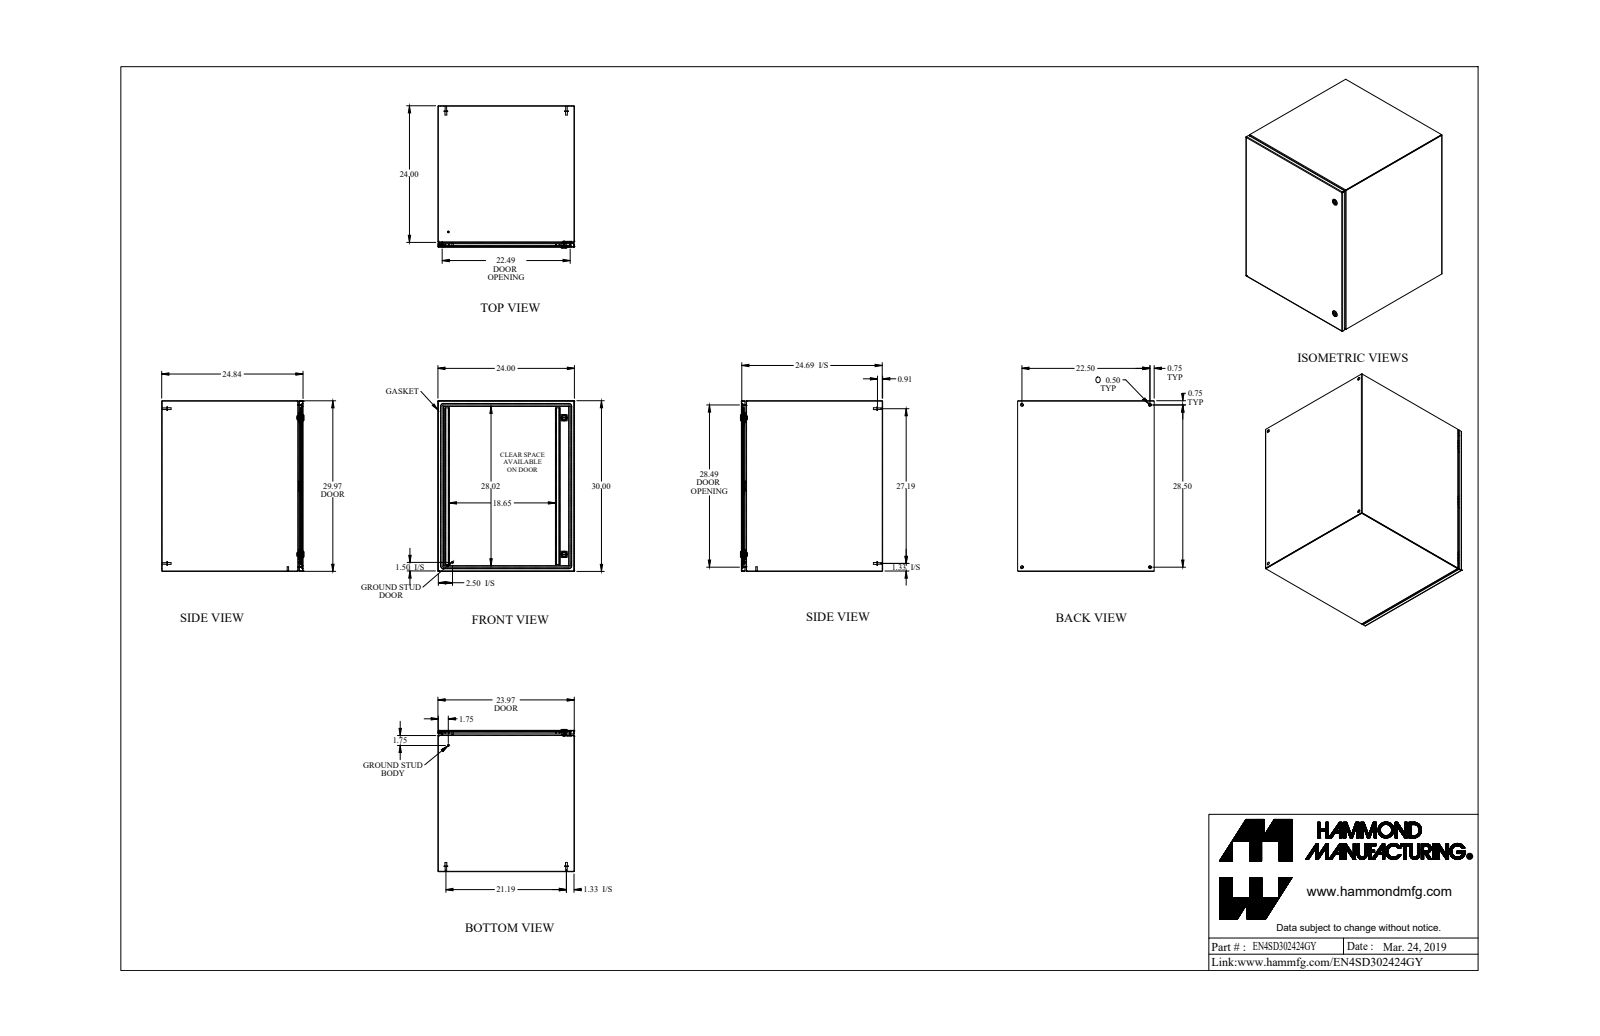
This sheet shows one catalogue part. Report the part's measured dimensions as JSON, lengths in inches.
{"part_name": "EN4SD302424GY", "step_written_by": "SolidWorks 2019 (AUTOMOTIVE_DESIGN)", "units": "inches", "bodies": {"solids": 33, "faces": 838, "planar": 399, "cylindrical": 283, "other": 156}, "overall_size": [30, 24.997, 24], "volume_in3": 319.1, "surface_area_in2": 8936, "round_holes": [[0.5, 4], [0.232, 2], [0.625, 2], [0.785, 2], [0.172, 1], [0.24, 1], [0.242, 1]], "round_bosses_or_shafts": [[0.625, 4], [0.313, 4], [0.27, 4], [1.1, 2], [0.525, 2], [0.281, 2], [0.25, 2], [0.455, 1]], "partial_cylinders_radius": [[0.036, 14], [0.108, 14], [0.043, 12], [0.081, 12], [0.312, 12], [0.1, 8], [0.006, 6], [0.062, 6]], "face_to_face_distances": [0.072, 23.928, 24.765, 29.928, 23.856, 24, 24.693, 24.837, 29.856, 30], "hole_center_spacings": [22.5, 28.5, 36.311, 2.493, 2.494, 21.545, 21.545, 23.999]}
